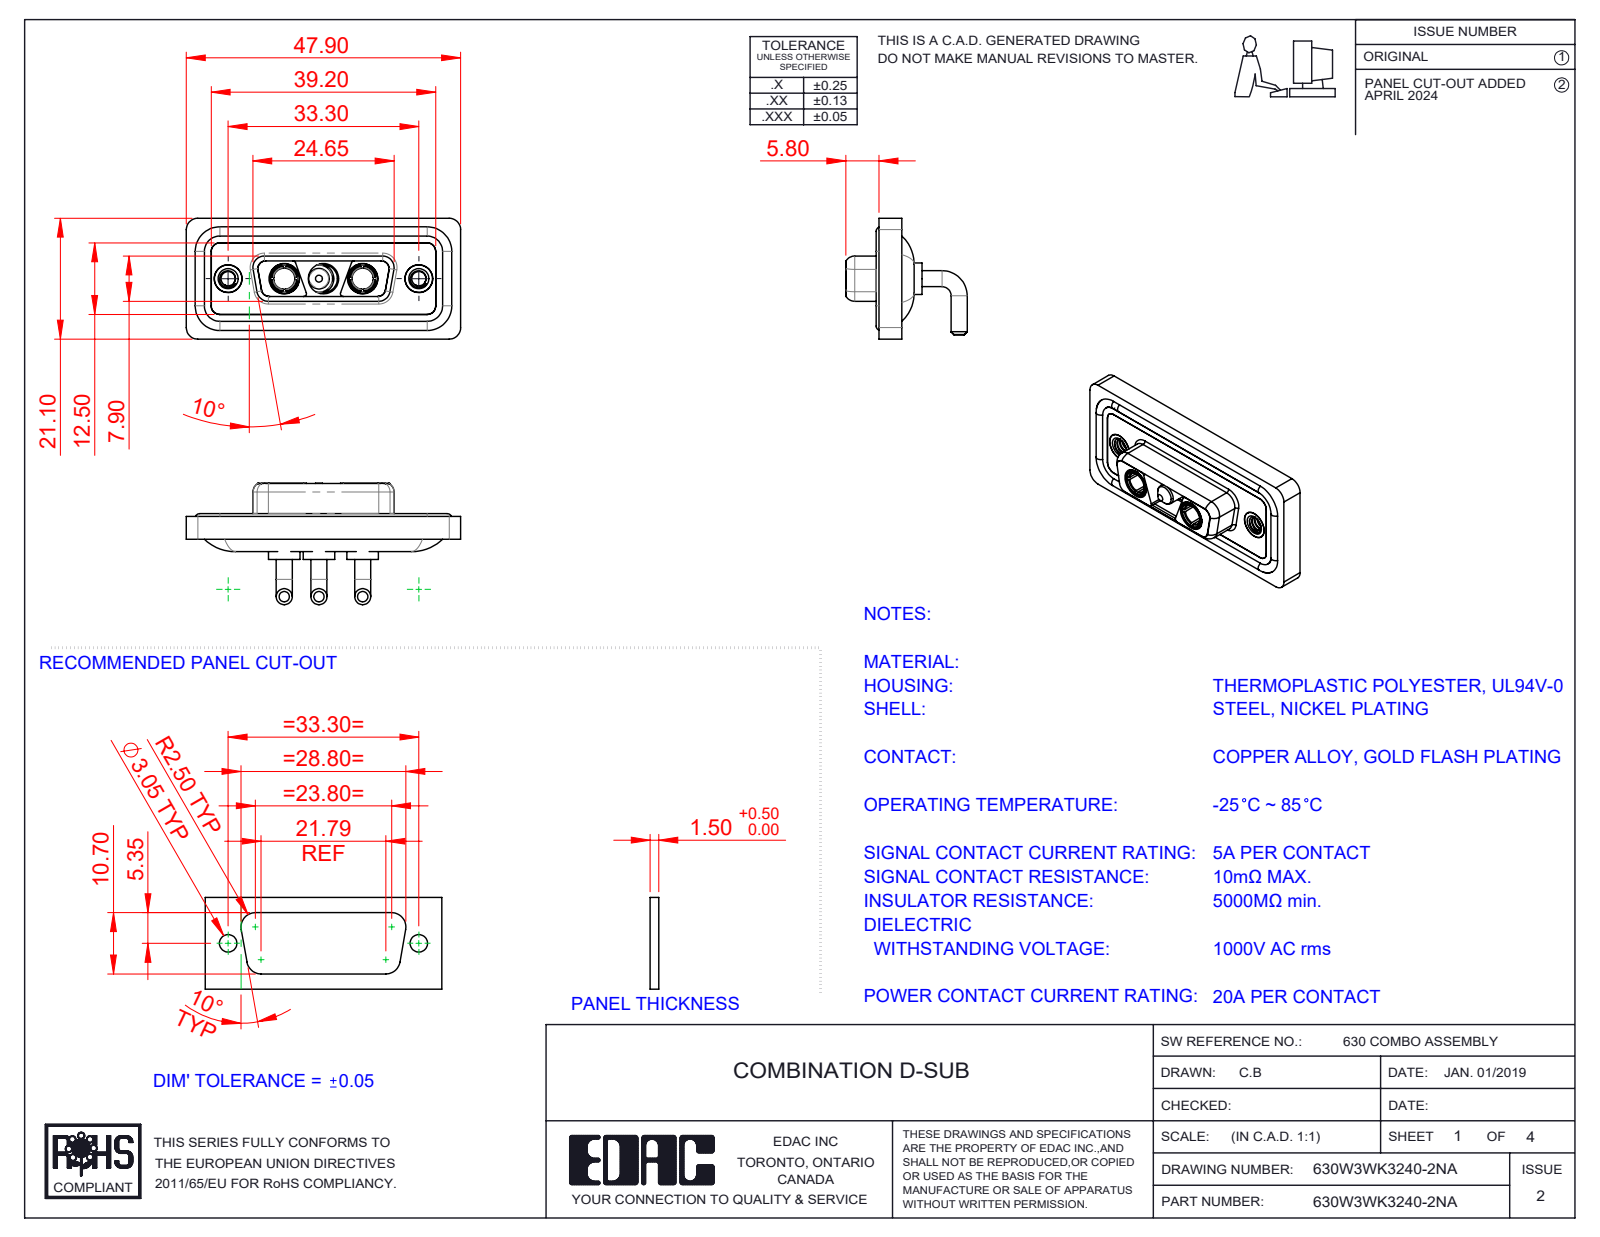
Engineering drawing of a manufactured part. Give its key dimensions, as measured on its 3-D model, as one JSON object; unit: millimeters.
{"part_name": "630Combo Threaded Rivet_A; 630Combo Shell Front_15 Contacts; Power Socket_20A RA; 630Combo Waterproof Housing_15 Contacts (+4 more)", "step_written_by": "SolidWorks 2023 (CONFIG_CONTROL_DESIGN)", "units": "millimeters", "bodies": {"solids": 13, "faces": 589, "planar": 178, "cylindrical": 262, "other": 149}, "overall_size": [47.9, 21.2, 21.1], "volume_mm3": 6024, "surface_area_mm2": 9741, "round_holes": [[4.85, 5], [5.3, 3], [2.5, 2], [3.7, 2], [4, 2], [4.05, 2], [5, 2]], "round_bosses_or_shafts": [[2.8, 6], [1.6, 4], [5.5, 3], [5.2, 3], [4.75, 3], [3.75, 3], [4.96, 2], [4.95, 2]], "partial_cylinders_radius": [[2, 20], [1.5, 18], [1.35, 12], [0.5, 8], [1.6, 8], [0.25, 4], [0.6, 4], [0.65, 4]], "face_to_face_distances": [0.4, 1.8, 1.1, 1.6, 2.9, 2.5, 3.1, 3.7, 4.1, 1.5], "hole_center_spacings": [6.85, 9.8, 16.65, 23.5, 13.7, 33.3]}
